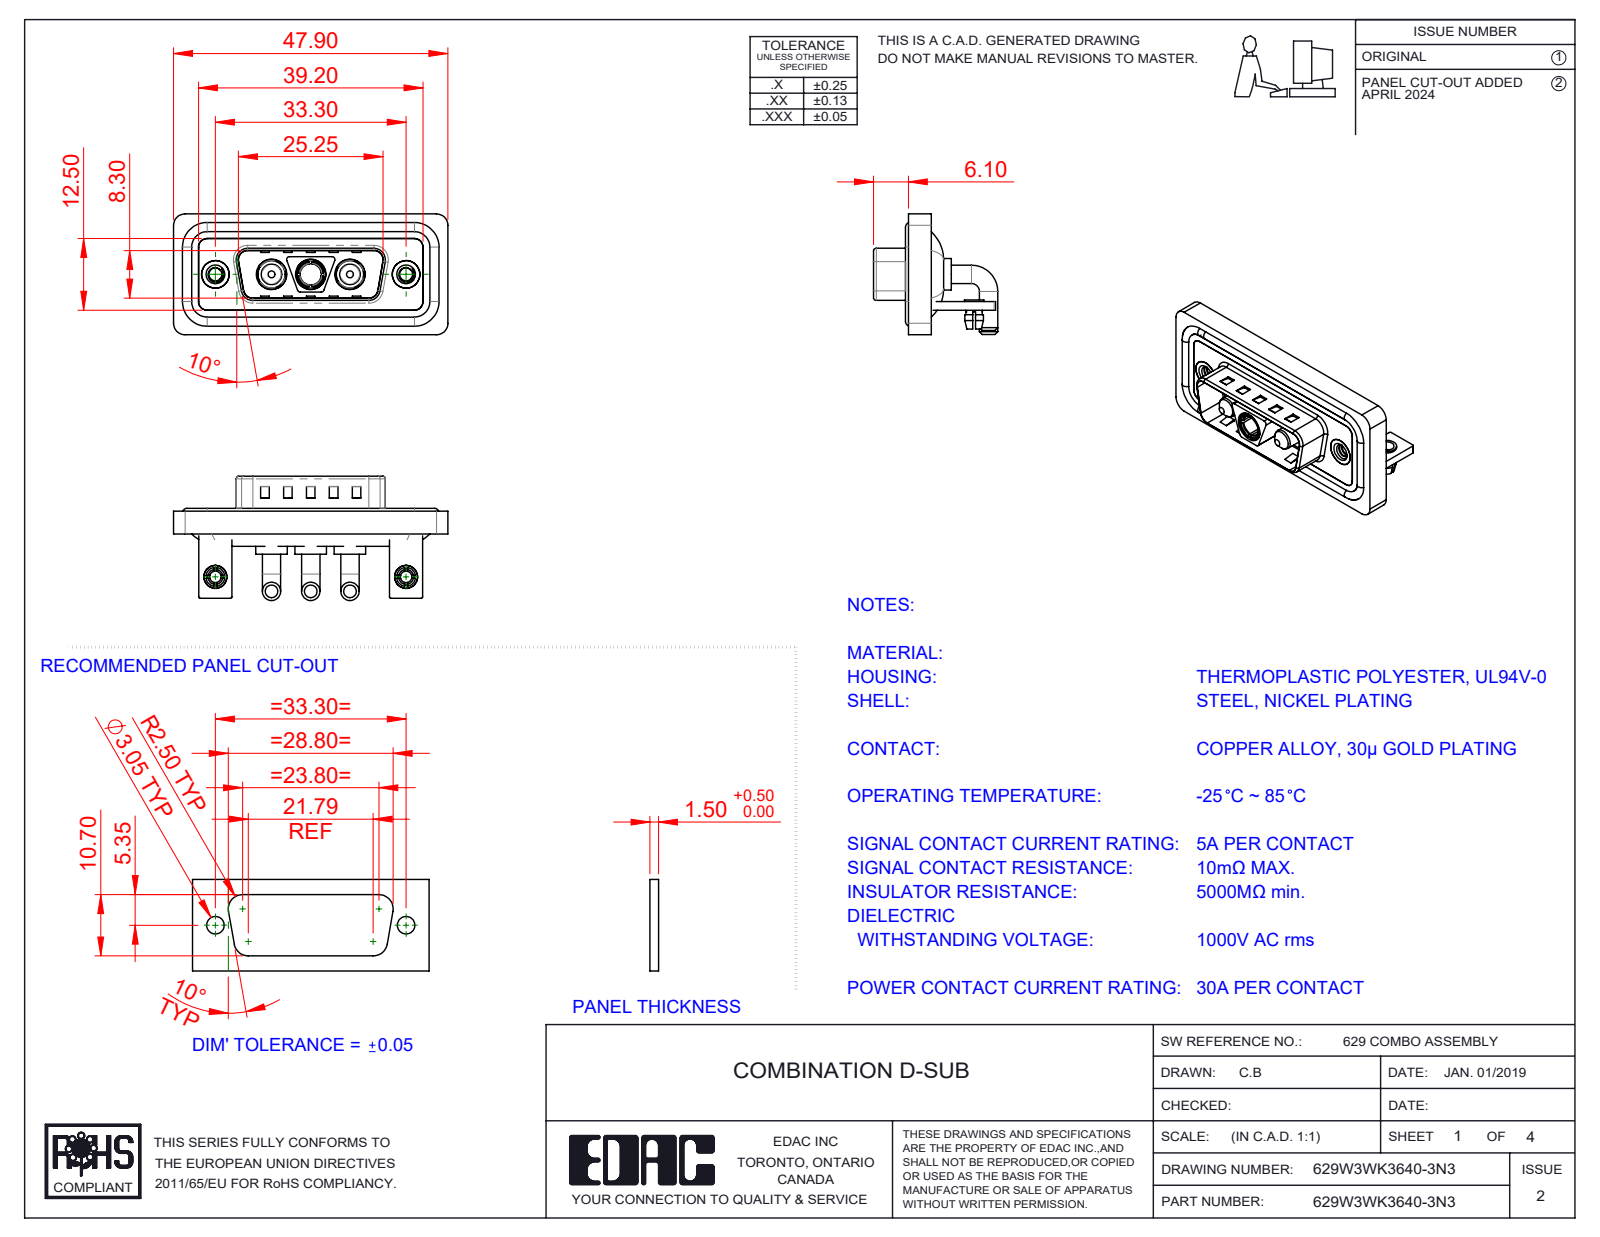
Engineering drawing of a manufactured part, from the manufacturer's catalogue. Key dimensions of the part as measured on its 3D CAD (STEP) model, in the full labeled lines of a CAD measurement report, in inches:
Part name (STEP PRODUCT): 629Combo Threaded Rivet_3; Power Socket_30A RA; 629W3WK3640-3N3; 629Combo Shell Rear_15 Contacts (+6 more)
STEP written by: SolidWorks 2023 (CONFIG_CONTROL_DESIGN)
Units: inches
Bodies: 17 solids, 753 faces (299 planar, 306 cylindrical, 148 other)
Overall size (bounding box): 1.886 × 0.854 × 0.831
Volume: 0.383 in³ · Surface area: 15.92 in²
Round holes (diameter × count): ⌀0.191 ×3, ⌀0.209 ×3, ⌀0.079 ×2, ⌀0.089 ×2, ⌀0.098 ×2, ⌀0.126 ×2, ⌀0.157 ×2, ⌀0.189 ×2, ⌀0.197 ×2, ⌀0.146 ×1
Round bosses / shafts (diameter × count): ⌀0.126 ×6, ⌀0.063 ×4, ⌀0.217 ×3, ⌀0.205 ×3, ⌀0.187 ×3, ⌀0.148 ×3, ⌀0.193 ×2, ⌀0.157 ×2
Partial cylindrical surfaces — rounded edges, fillets, slot ends (radius × count): R0.079 ×21, R0.059 ×18, R0.01 ×16, R0.02 ×13, R0.063 ×8, R0.024 ×4, R0.026 ×4, R0.035 ×4
Main face-to-face distances: 0.016, 0.059, 0.031, 0.114, 0.043, 0.083, 0.146, 0.063, 0.047, 0.177
Hole centre spacings: 0.27, 0.386, 0.656, 0.925, 1.311, 0.539
